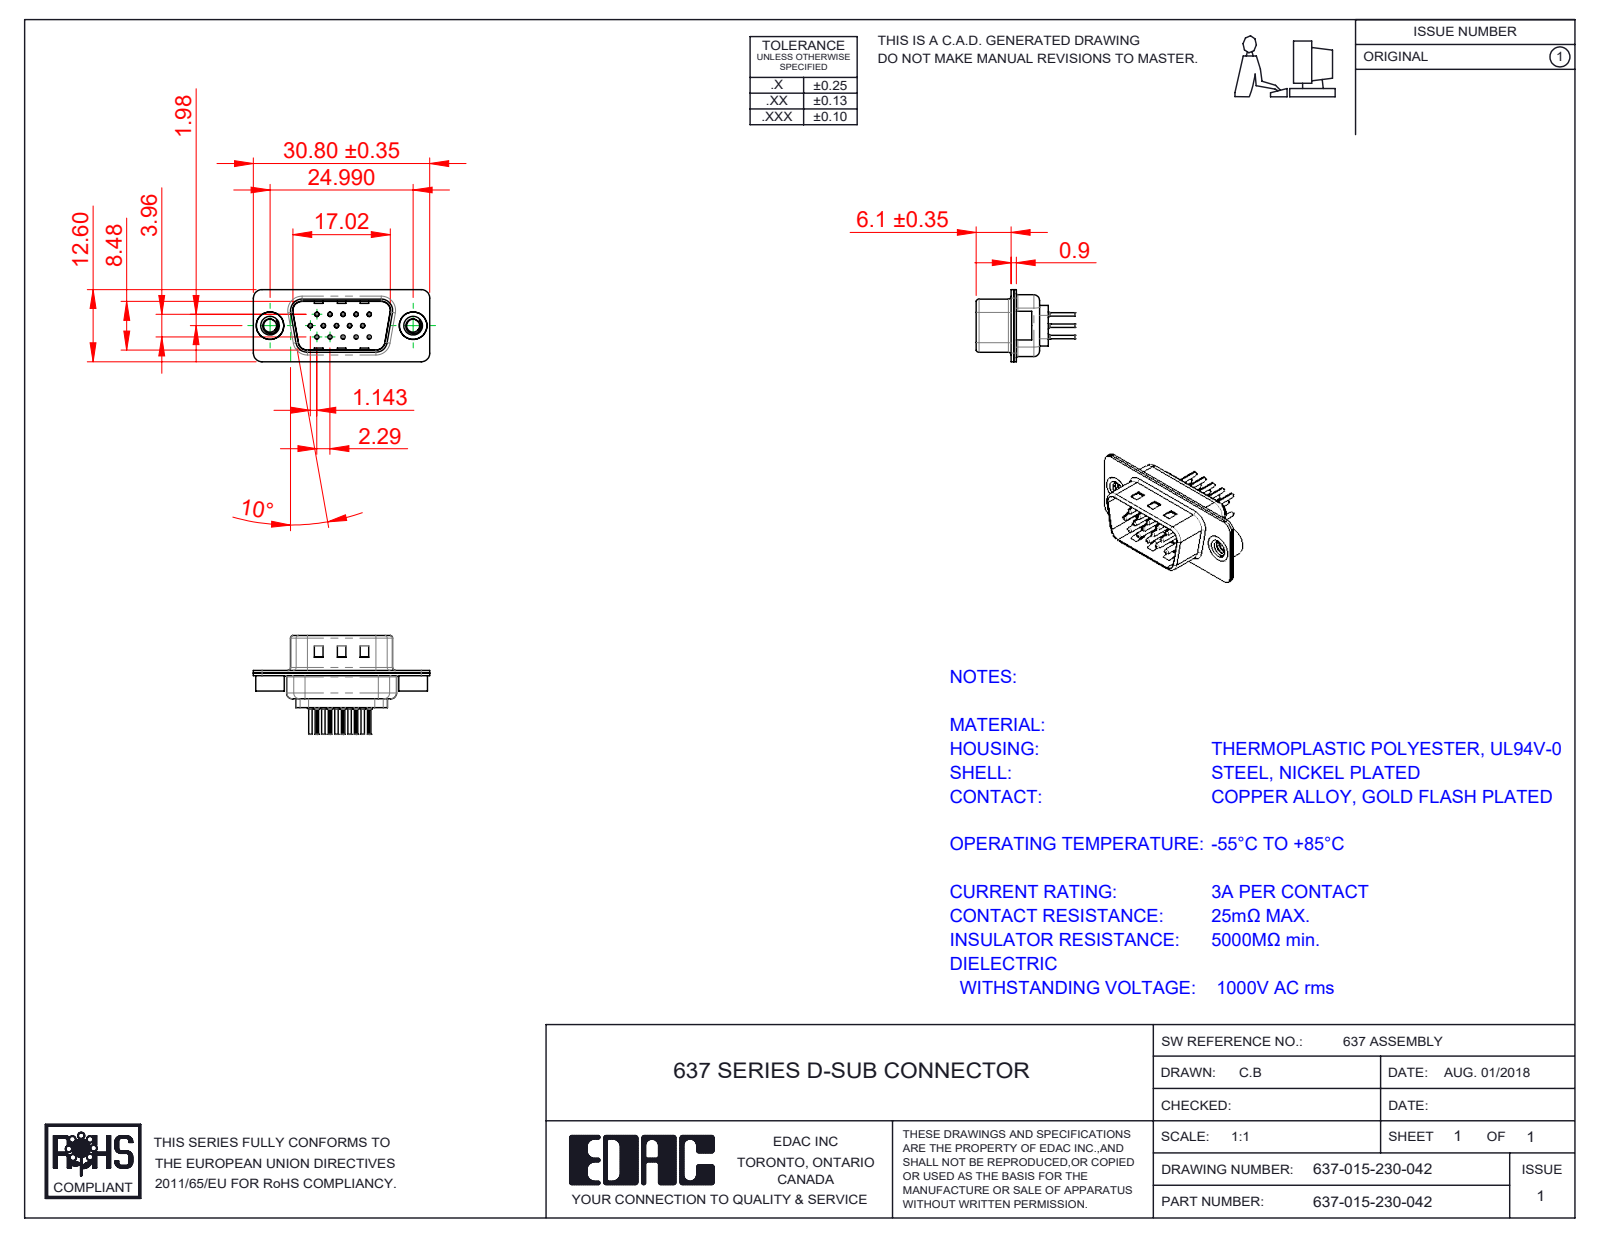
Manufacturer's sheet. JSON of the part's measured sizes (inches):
{"part_name": "637 Contact Row 2_30; 637 Contact Row 1_30; 637 Contact Row 3_30; 637-015-230-062 (+4 more)", "step_written_by": "SolidWorks 2020 (CONFIG_CONTROL_DESIGN)", "units": "inches", "bodies": {"solids": 20, "faces": 1804, "planar": 467, "cylindrical": 684, "other": 653}, "overall_size": [1.213, 0.679, 0.496], "volume_in3": 0.08, "surface_area_in2": 7.203, "round_holes": [[0.008, 15], [0.014, 15], [0.043, 15], [0.063, 15], [0.089, 2], [0.157, 2], [0.189, 2]], "round_bosses_or_shafts": [[0.079, 15], [0.059, 15], [0.03, 15], [0.024, 15], [0.197, 2], [0.193, 2]], "partial_cylinders_radius": [[0.004, 30], [0.059, 16], [0.079, 12], [0.02, 8], [0.01, 4], [0.022, 4], [0.028, 4], [0.037, 4]], "face_to_face_distances": [0.018, 0.035, 0.016, 0.028, 0.35, 0.334, 0.041, 0.012, 0.179, 0.046], "hole_center_spacings": [0.156, 0.09, 0.18, 0.09, 0.238, 0.27, 0.312, 0.238]}
